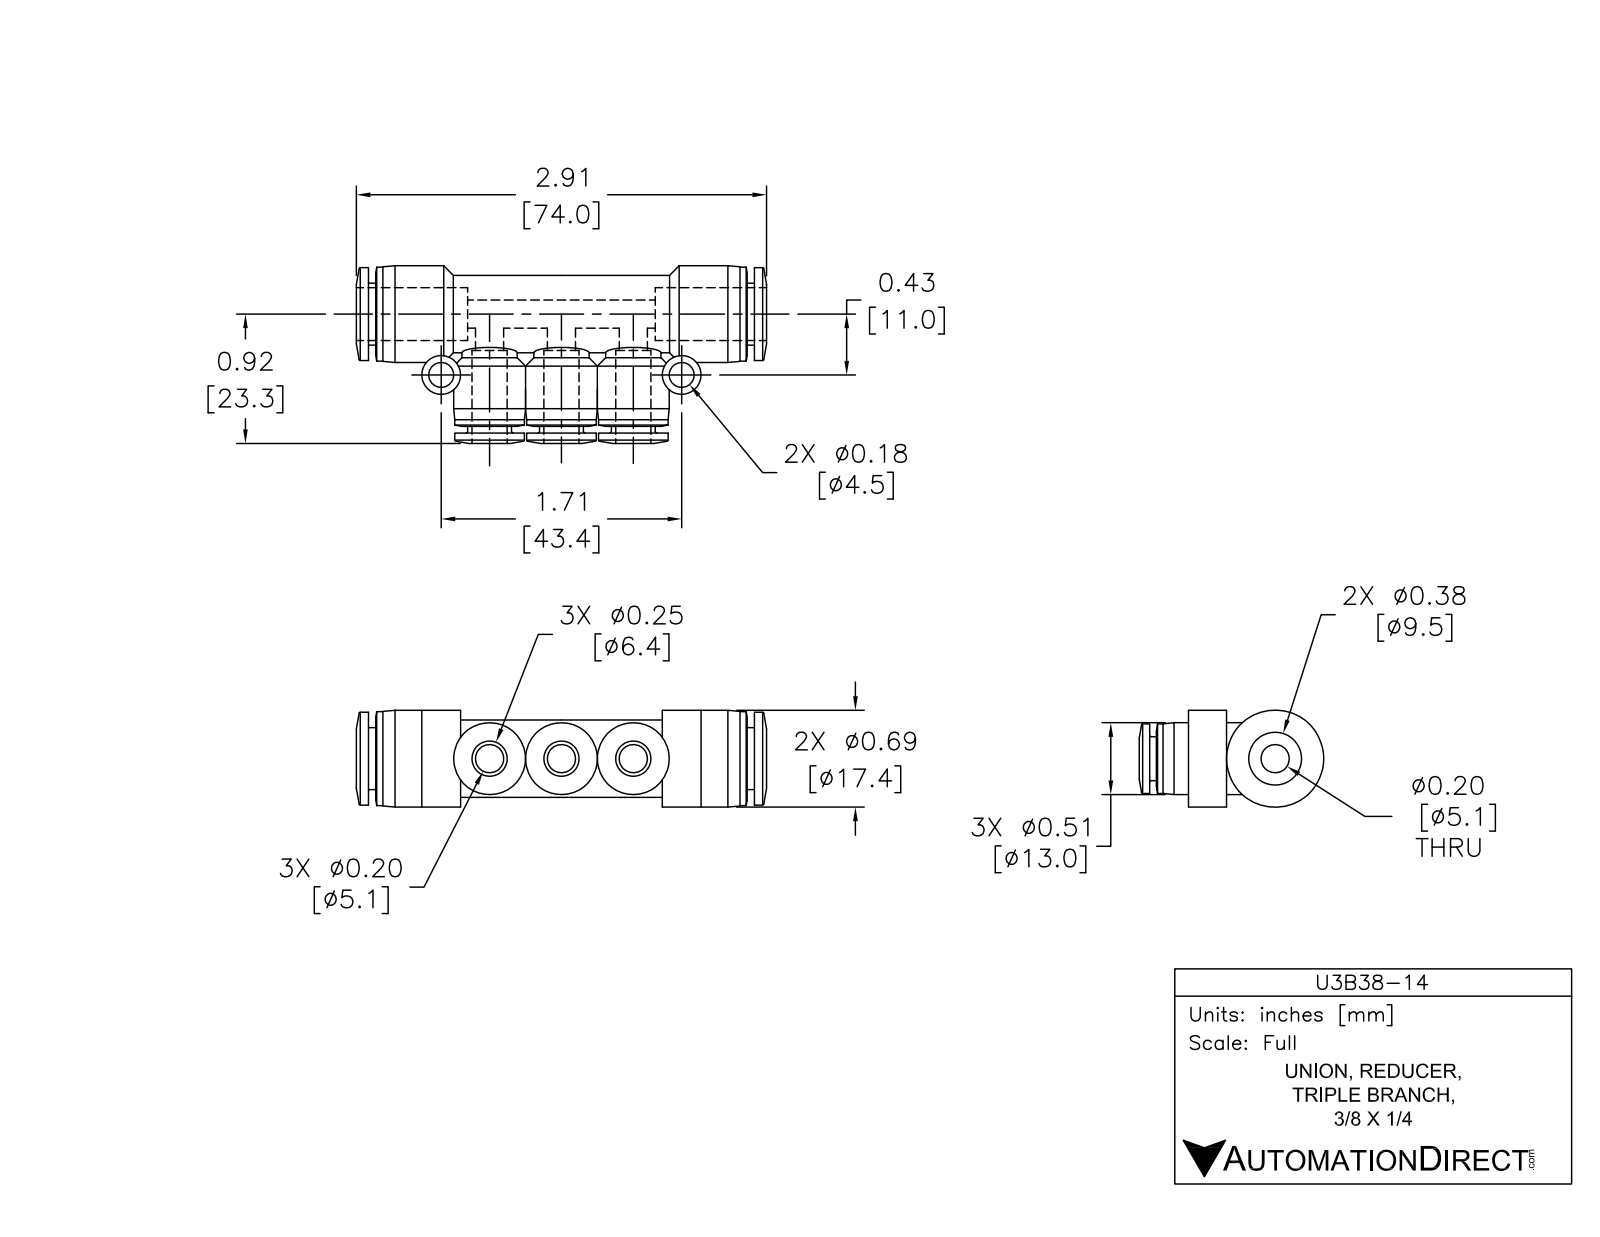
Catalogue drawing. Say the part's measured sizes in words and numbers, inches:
The part is named "U3B38-14". Its 3-D file was written by "SolidWorks 2015 (AUTOMOTIVE_DESIGN)". It is 1 solid with 171 faces: 21 planar, 74 cylindrical and 76 other. Overall it measures 2.921 by 1.266 by 0.689 inches. Its volume is 0.897 cubic inches and its surface area 16.99 square inches. Round holes: 4 of diameter 0.189, 3 of diameter 0.258, 2 of diameter 0.177, 1 of diameter 0.386. Round bosses or shafts: 3 of diameter 0.512, 3 of diameter 0.496, 3 of diameter 0.394, 3 of diameter 0.313, 2 of diameter 0.276, 1 of diameter 0.689, 1 of diameter 0.669, 1 of diameter 0.661. The main face-to-face distances are 0.051, 2.697, 2.748, 0.705, 2.043, 0.654, 1.992, 0.047, 2.646, 1.339. The hole center spacings are 0.512, 1.024, 1.713.
